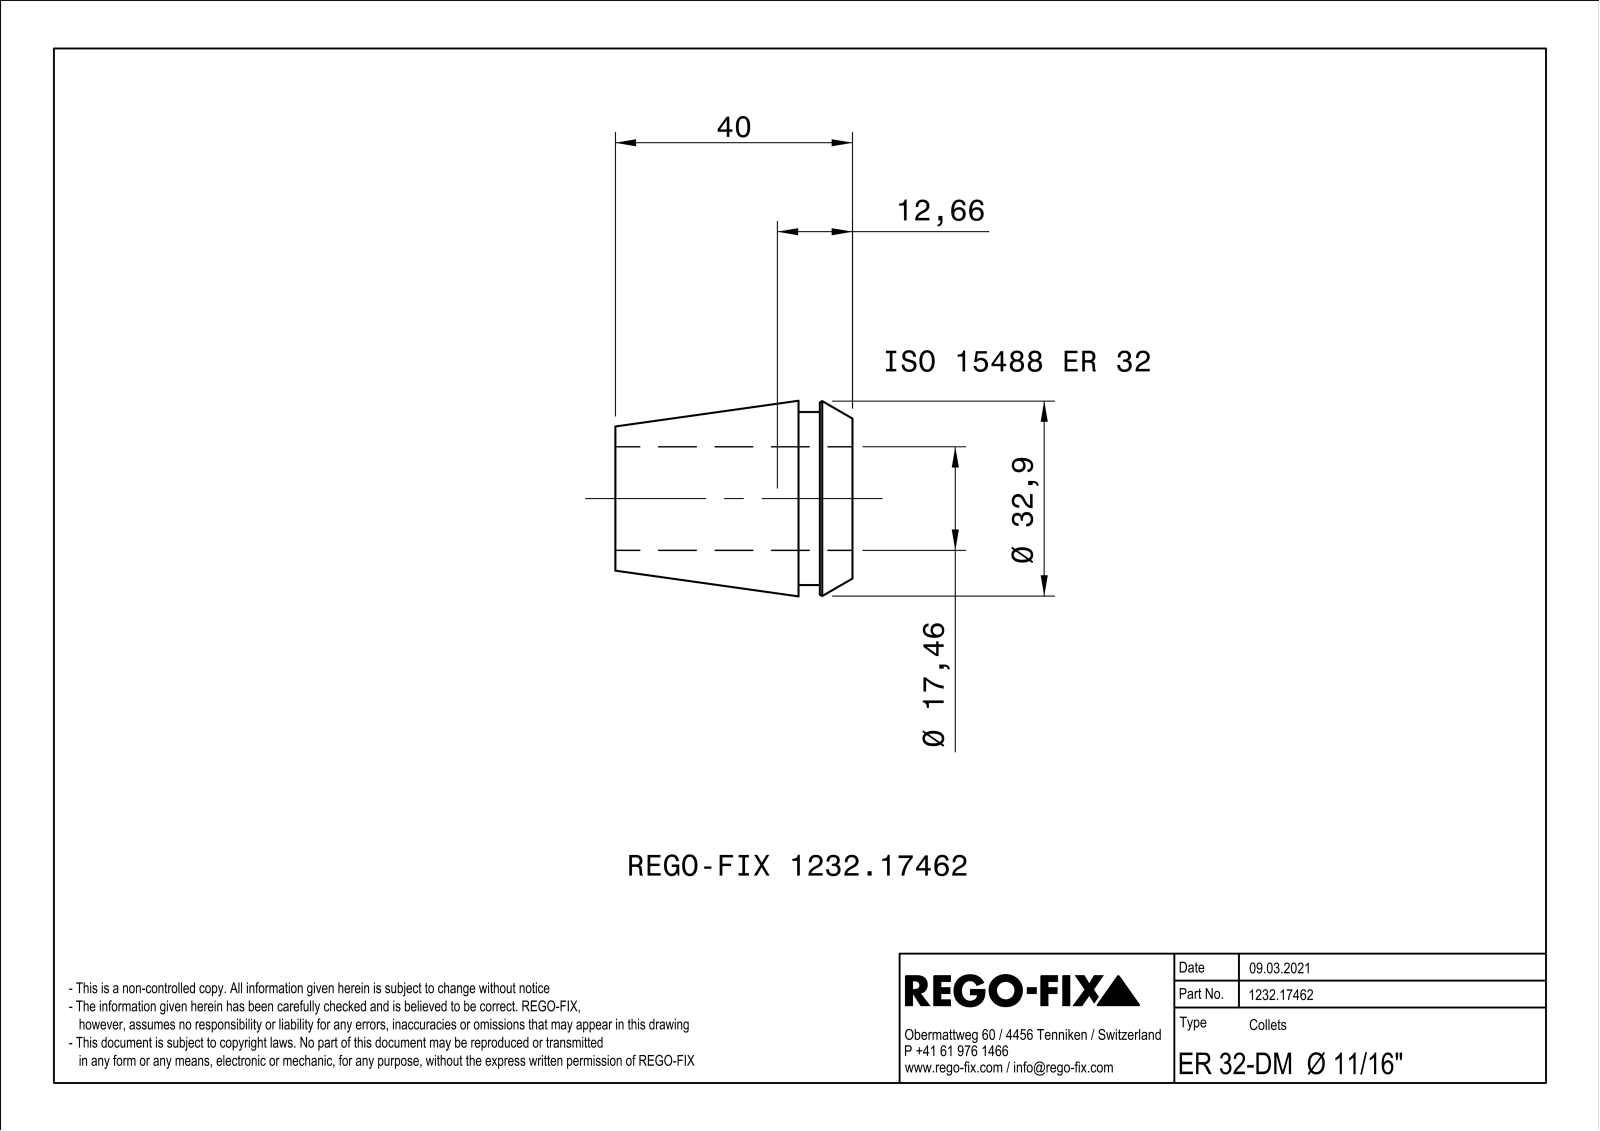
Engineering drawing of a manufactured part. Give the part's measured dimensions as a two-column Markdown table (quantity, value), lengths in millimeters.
| quantity | value |
| --- | --- |
| part name | NOCUT |
| STEP written by | SIEMENS PLM Software Solid Edge ST10 (AUTOMOTIVE_DESIGN) |
| units | millimeters |
| bodies | 1 solid, 154 faces (80 planar, 9 cylindrical, 65 other) |
| overall size | 40 × 32.98 × 32.98 |
| volume | 14 186 mm³ |
| surface area | 11 172 mm² |
| round holes (diameter × count) | 17.46 × 1 |
| round bosses / shafts (diameter × count) | 29.2 × 1 |
| main face-to-face distances | 1, 40, 9.1, 30.9, 5.5, 3.6, 34.5, 16, 10.5, 6.9 |
